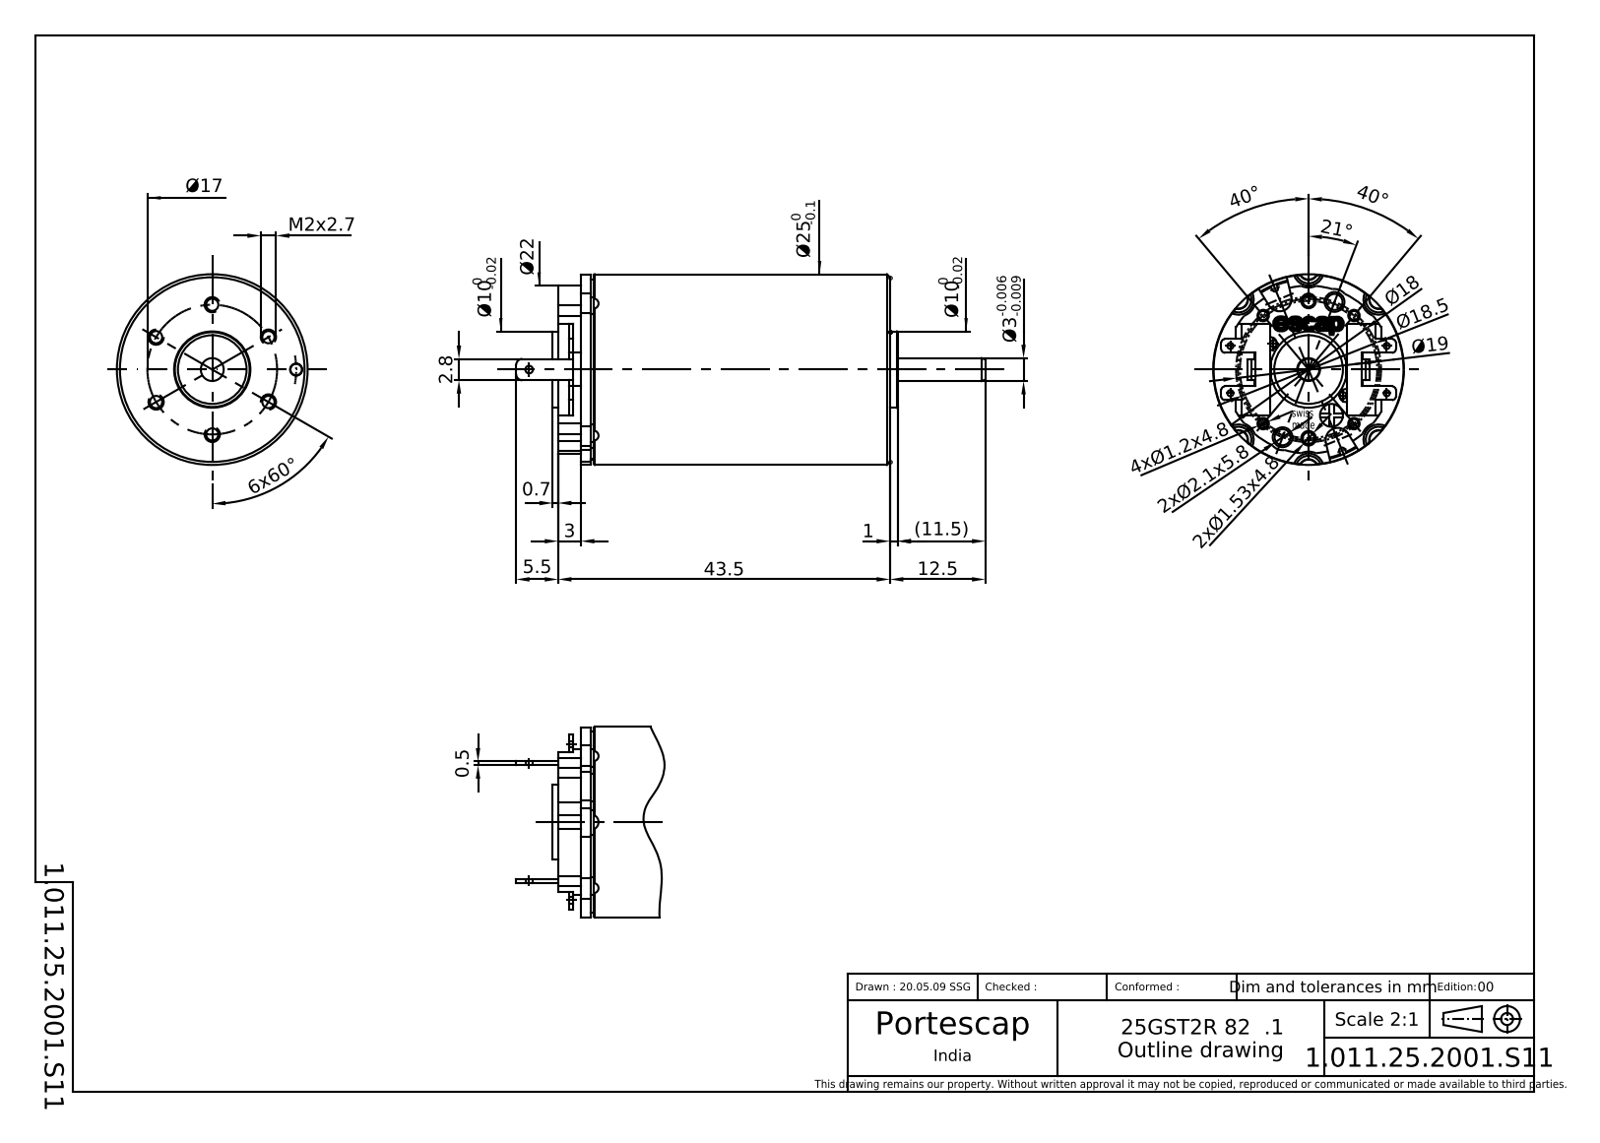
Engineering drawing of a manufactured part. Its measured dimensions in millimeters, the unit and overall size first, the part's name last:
Units: millimetres
Overall size (bounding box): 61.5 × 25.5 × 25.5
Round holes (diameter × count): ⌀1.6 ×6, ⌀1.5 ×5, ⌀0.8 ×4, ⌀1.2 ×4, ⌀1.53 ×2, ⌀1.93 ×2, ⌀2 ×2, ⌀2.6 ×2, ⌀1 ×1, ⌀3 ×1
Round bosses / shafts (diameter × count): ⌀25.5 ×1, ⌀25 ×1, ⌀24 ×1, ⌀10 ×1, ⌀9 ×1, ⌀3 ×1
Partial cylindrical surfaces — rounded edges, fillets, slot ends (radius × count): R0.5 ×12, R2.25 ×6, R1.6 ×2, R1.81 ×2, R11 ×1
Main face-to-face distances: 1.5, 40.5, 43.5, 3, 1, 42, 41.5, 43, 44.5, 4.4
Hole centre spacings: 8.5, 14.72, 3.06, 3.17, 5.83, 6.11, 6.25, 7.88
Volume: 20 787 mm³ · Surface area: 5 125 mm²
Bodies: 1 solid, 233 faces (95 planar, 110 cylindrical, 28 other)
Part name (STEP PRODUCT): 25GST2R_82_216P_1
STEP written by: PRO/ENGINEER BY PARAMETRIC TECHNOLOGY CORPORATION, 2014310 (CONFIG_CONTROL_DESIGN)
